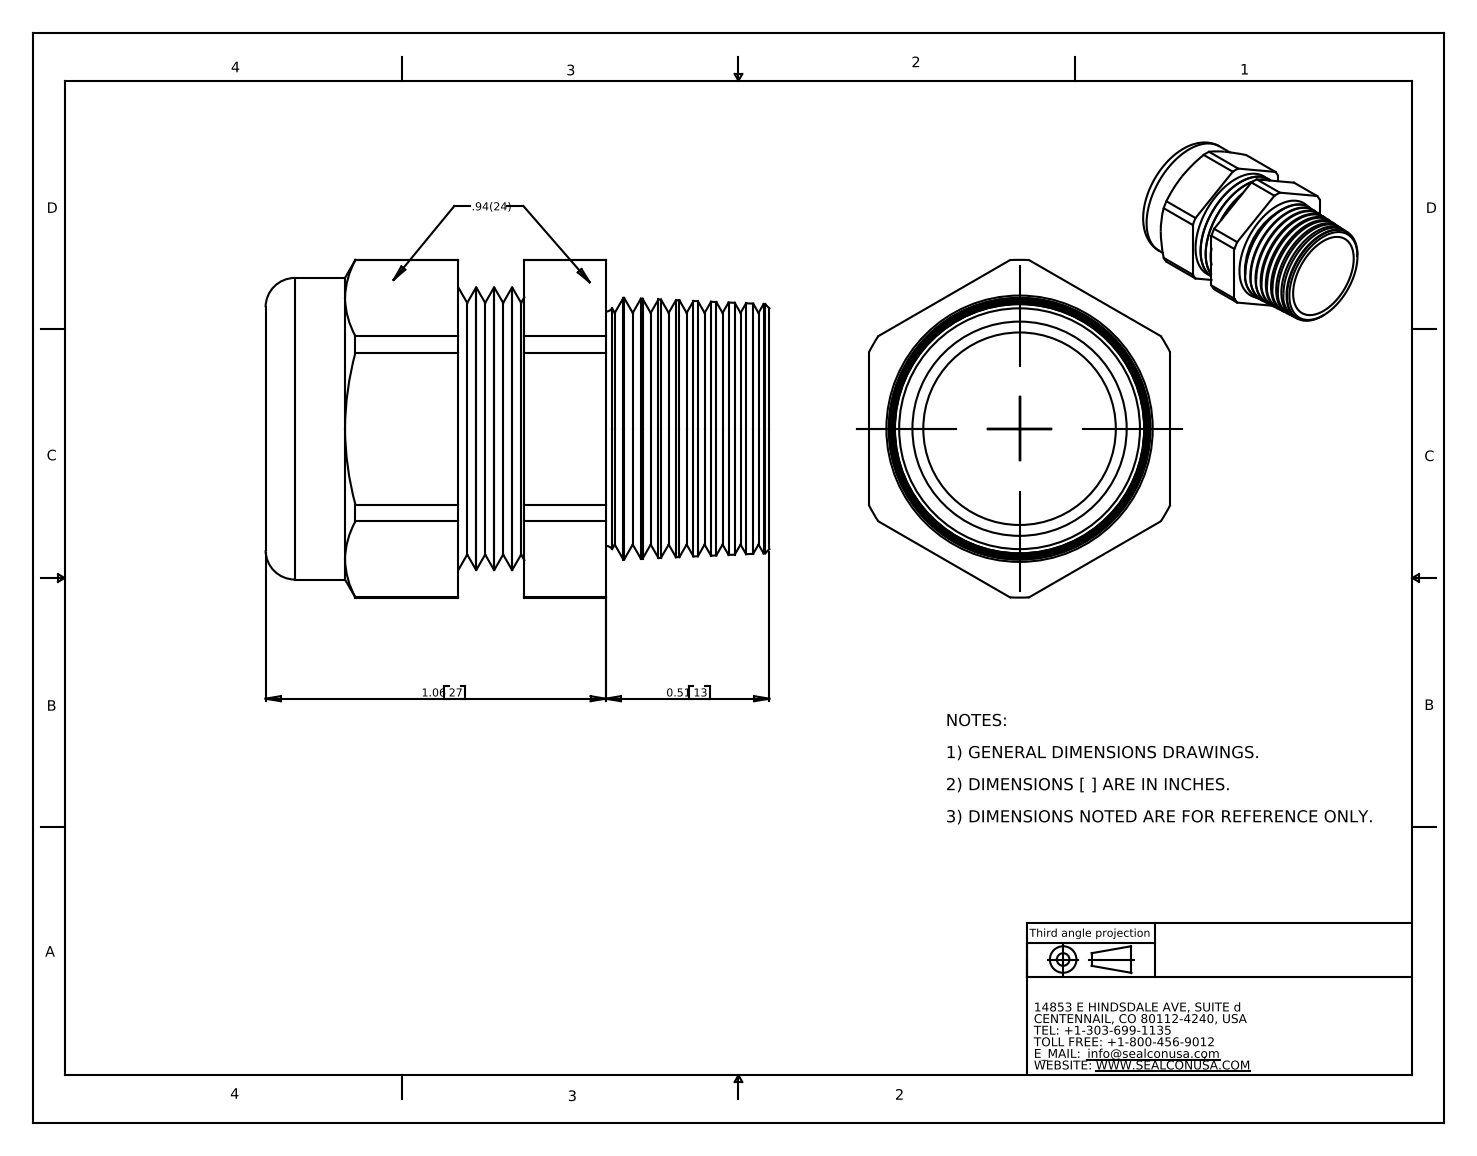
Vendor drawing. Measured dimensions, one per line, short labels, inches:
name: CD13NA-GY
written by: SolidWorks 2007 (CONFIG_CONTROL_DESIGN)
unit: in
bodies: 2 solids, 138 faces (20 planar, 30 cylindrical, 88 other)
size: 1.57 × 1.053 × 0.94
volume: 0.494 in³; area: 11.42 in²
holes: 1× ⌀0.6, 1× ⌀0.697
bosses: 1× ⌀0.94, 1× ⌀0.88
rounds: 1× R0.526
face distances: 0.94, 0.813, 0.354, 0.459, 0.559, 0.206, 0.254, 1.322, 0.969, 0.763
